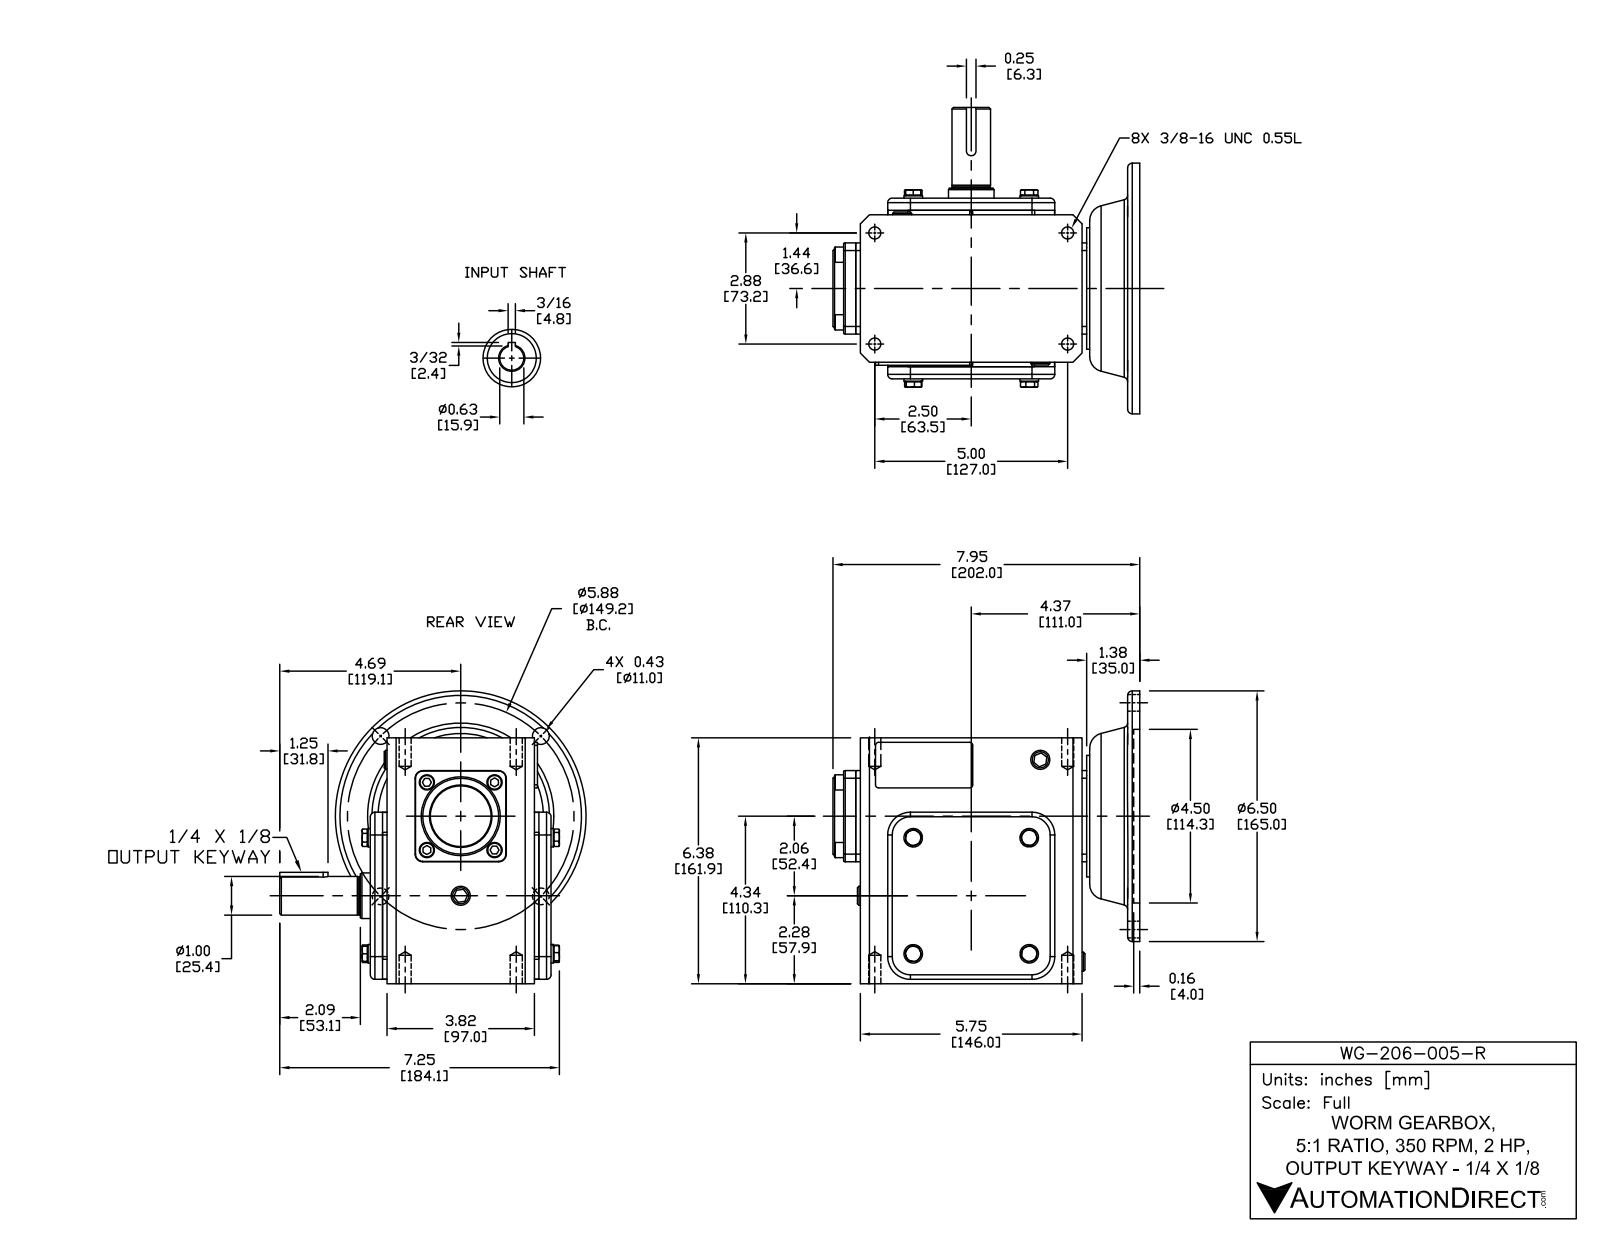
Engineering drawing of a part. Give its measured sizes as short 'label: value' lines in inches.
name: WG-206-005-R
written by: SolidWorks 2015 (CONFIG_CONTROL_DESIGN)
unit: in
bodies: 43 solids, 610 faces (300 planar, 182 cylindrical, 128 other)
size: 7.953 × 7.938 × 7.591
volume: 171.8 in³; area: 407.7 in²
holes: 4× ⌀0.313, 4× ⌀0.406, 1× ⌀0.591, 1× ⌀0.625, 1× ⌀1.181, 1× ⌀1.457, 1× ⌀1.654, 1× ⌀3.543, 1× ⌀4.5
bosses: 8× ⌀0.394, 4× ⌀0.48, 1× ⌀6.496, 1× ⌀3.15, 1× ⌀2.047, 1× ⌀1.575, 1× ⌀1.181, 1× ⌀1.142
rounds: 8× R0.079, 8× R0.118, 4× R0.197, 4× R0.591, 2× R0.02, 2× R0.039, 1× R0.125, 1× R2.717
face distances: 0.315, 0.118, 4.055, 4.37, 0.433, 4.252, 3.937, 6.375, 4.685, 0.709
hole spacings: 2.937, 4.154, 2.077, 2.88, 4.631, 5, 5.77, 5.875
